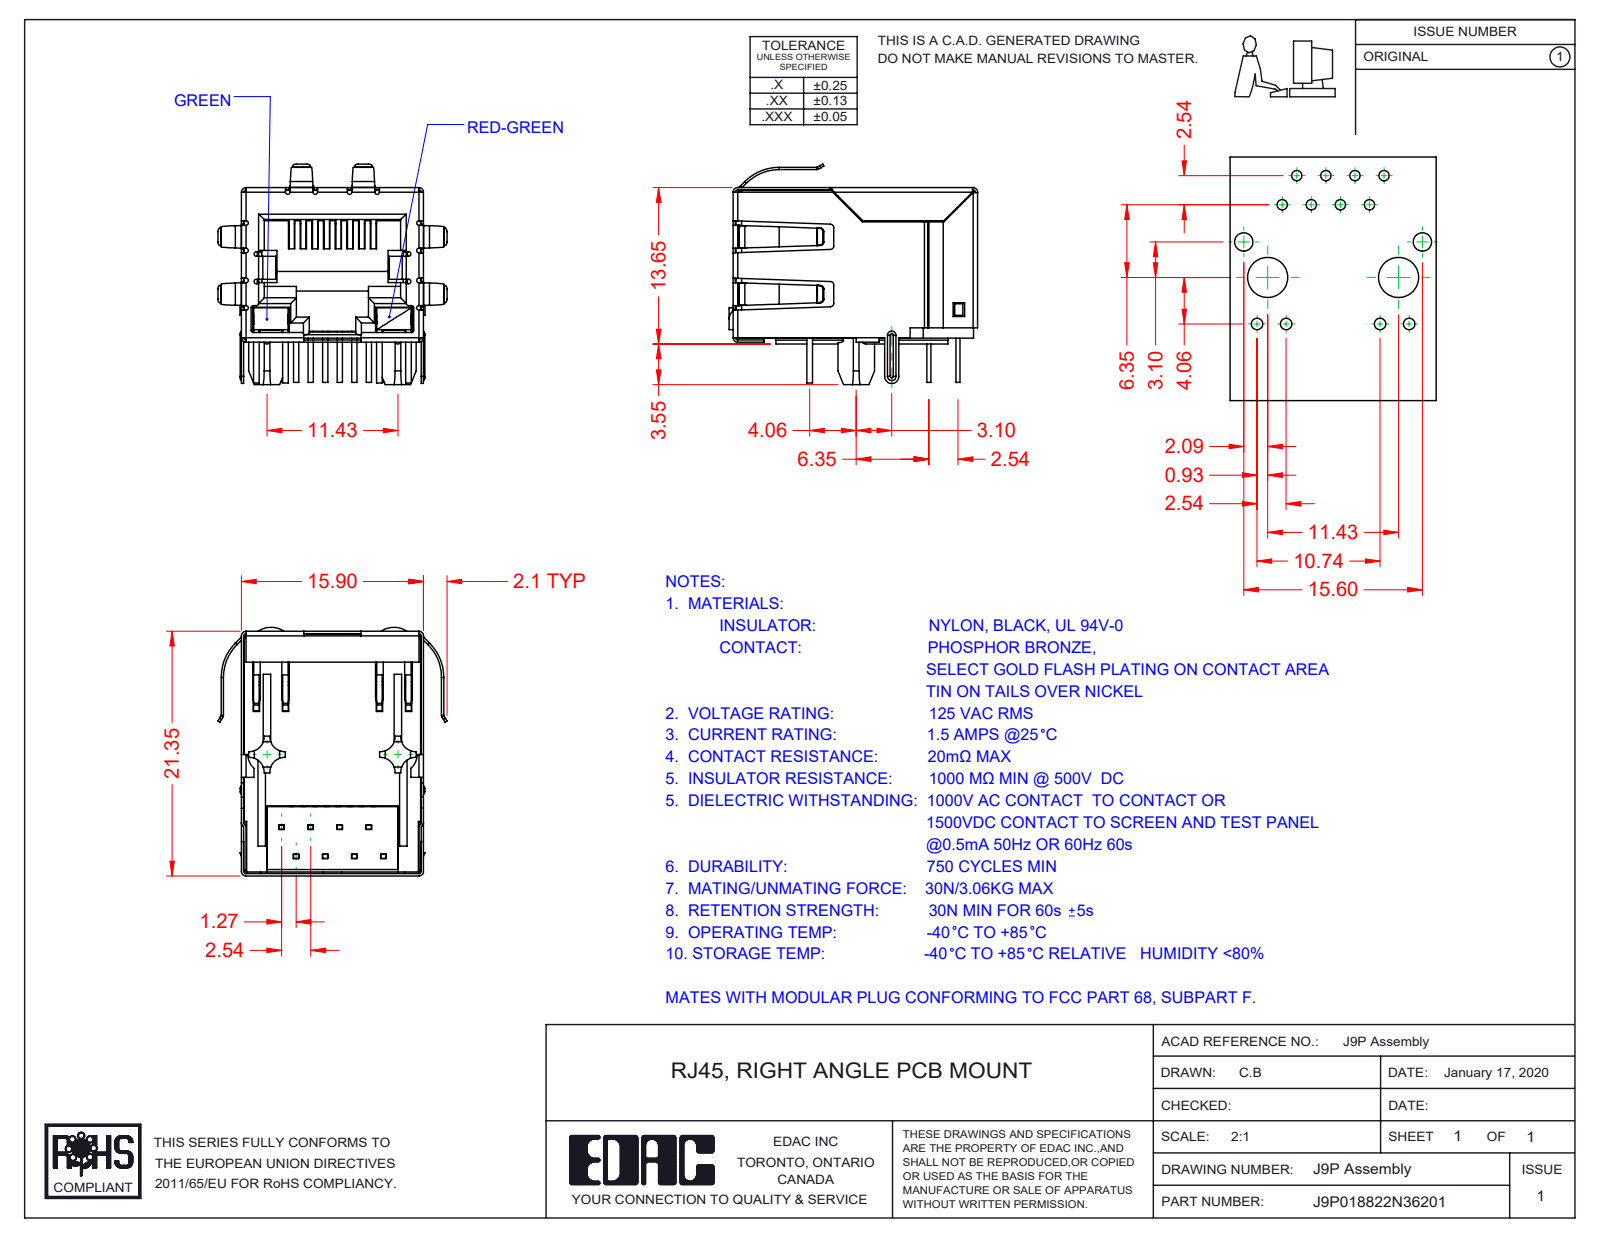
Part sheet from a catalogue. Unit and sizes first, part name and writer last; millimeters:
Units: millimetres
Overall size (bounding box): 21.7 × 20 × 19.25
Partial cylindrical surfaces — rounded edges, fillets, slot ends (radius × count): R0.2 ×39, R0.5 ×22, R0.3 ×20, R0.4 ×16, R1.3 ×8, R0.23 ×5, R0.11 ×4, R0.31 ×4
Main face-to-face distances: 15.45, 15.7, 15.65, 0.35, 0.54, 15.5, 12.36, 0.6, 1.4, 0.59
Volume: 2 687 mm³ · Surface area: 7 515 mm²
Bodies: 13 solids, 1474 faces (1042 planar, 338 cylindrical, 94 other)
Part name (STEP PRODUCT): 9P-LED Contact Lock; J9P018822N36202; 9P-LED LED RH_6-Red-Green; 9P-LED Insulator (+4 more)
STEP written by: SolidWorks 2016 (CONFIG_CONTROL_DESIGN)
